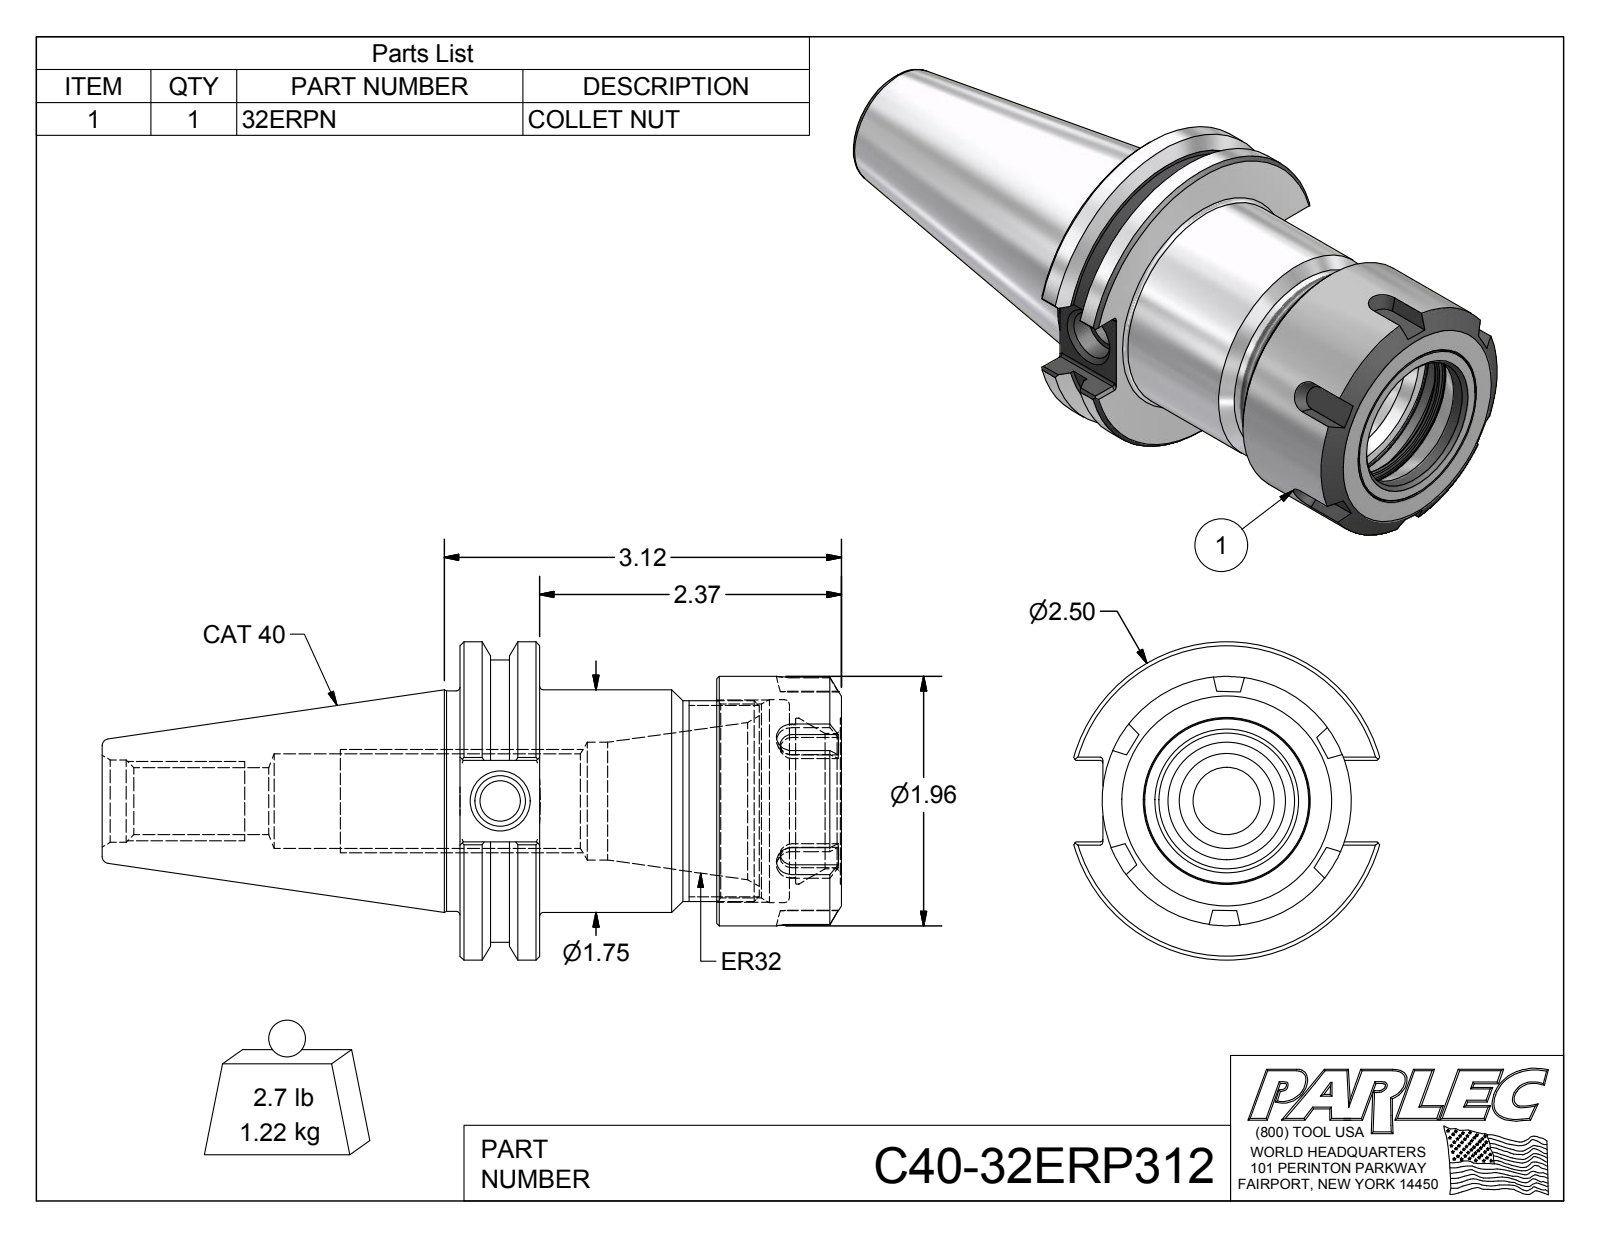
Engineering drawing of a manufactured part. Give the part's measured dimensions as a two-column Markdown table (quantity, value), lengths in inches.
| quantity | value |
| --- | --- |
| part name | C40-32ERP312; C40-32ER3-1; 32ERPN |
| STEP written by | Autodesk Inventor 2012 (AUTOMOTIVE_DESIGN) |
| units | inches |
| bodies | 2 solids, 129 faces (54 planar, 33 cylindrical, 42 other) |
| overall size | 5.808 × 2.5 × 2.403 |
| volume | 9.442 in³ |
| surface area | 60.56 in² |
| round holes (diameter × count) | 0.315 × 1, 0.399 × 1, 0.527 × 1, 0.648 × 1, 0.745 × 1, 0.925 × 1, 1.063 × 1, 1.2 × 1, 1.305 × 1, 1.523 × 1, 1.595 × 1 |
| round bosses / shafts (diameter × count) | 2.5 × 1, 2.219 × 1, 1.958 × 1, 1.75 × 1, 1.73 × 1, 1.575 × 1 |
| partial cylindrical surfaces (radius × count) | 0.02 × 12 |
| main face-to-face distances | 0.625, 2.995, 2.37, 2.017, 1.392, 0.978, 2.588, 1.963, 0.571, 0.407 |
